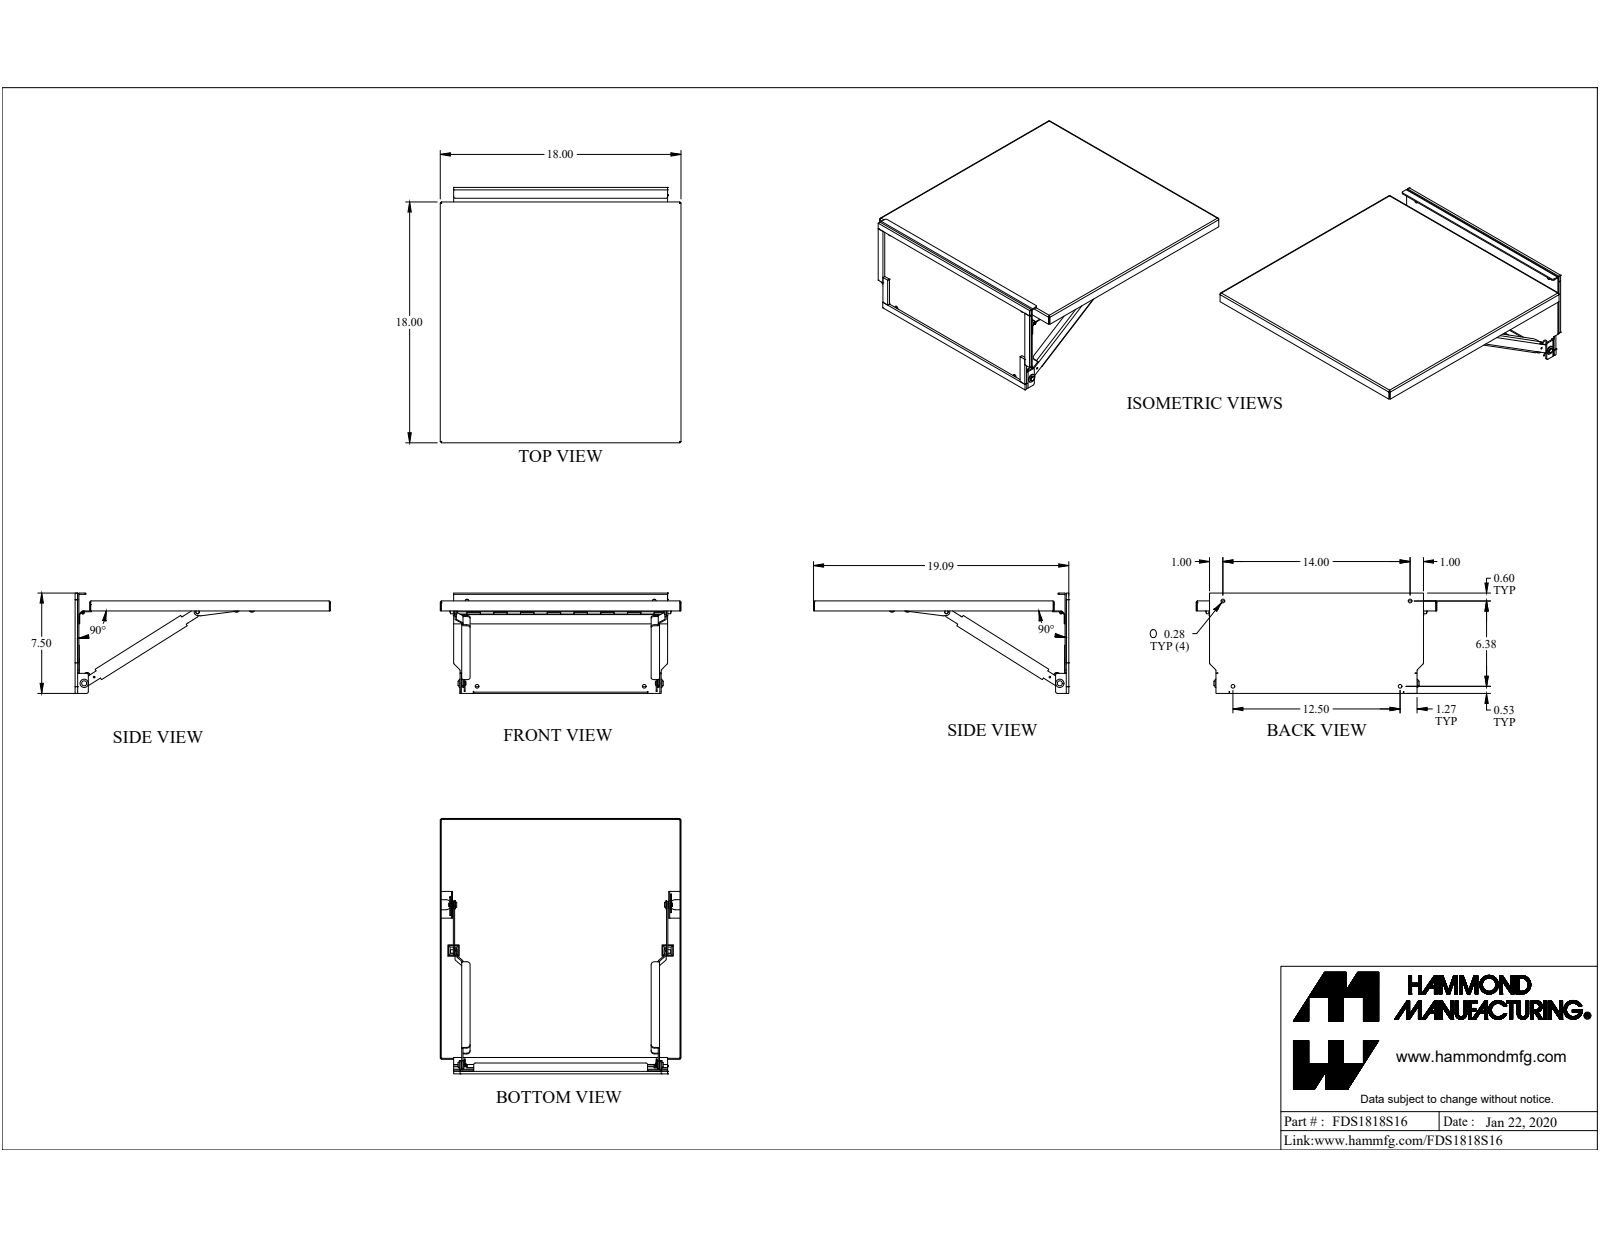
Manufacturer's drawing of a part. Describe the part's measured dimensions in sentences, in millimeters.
The part is named "FDS1818S16". Its 3-D file was written by "SolidWorks 2019 (CONFIG_CONTROL_DESIGN)". It is 42 solids with 624 faces: 381 planar, 194 cylindrical and 49 other. Overall it measures 484.9 by 457.2 by 190.5 millimeters. Its volume is 832 600 cubic millimeters and its surface area 836 800 square millimeters. Round holes: 4 of diameter 2.4, 4 of diameter 7.1, 3 of diameter 3.2, 3 of diameter 6.7, 3 of diameter 6.7, 2 of diameter 6.5, 2 of diameter 6.6, 2 of diameter 7.2, 1 of diameter 2.8. Round bosses or shafts: 3 of diameter 6.4, 2 of diameter 15.9, 2 of diameter 13, 2 of diameter 9.5, 1 of diameter 15.9, 1 of diameter 12.7, 1 of diameter 5.9, 1 of diameter 2.5. Partial cylindrical surfaces (rounded edges, fillets, slot ends): 16 of radius 6.4, 12 of radius 1.2, 12 of radius 3.6, 11 of radius 3.2, 6 of radius 0.9, 6 of radius 2.7, 6 of radius 9.5, 4 of radius 1.3. The main face-to-face distances are 1.8, 2.4, 455.4, 22.3, 1.6, 457.2, 7.2, 4.7, 24.7, 29.5. The hole center spacings are 87.1, 163, 218, 305.2, 373.5, 422.4, 442.5, 496.2.
